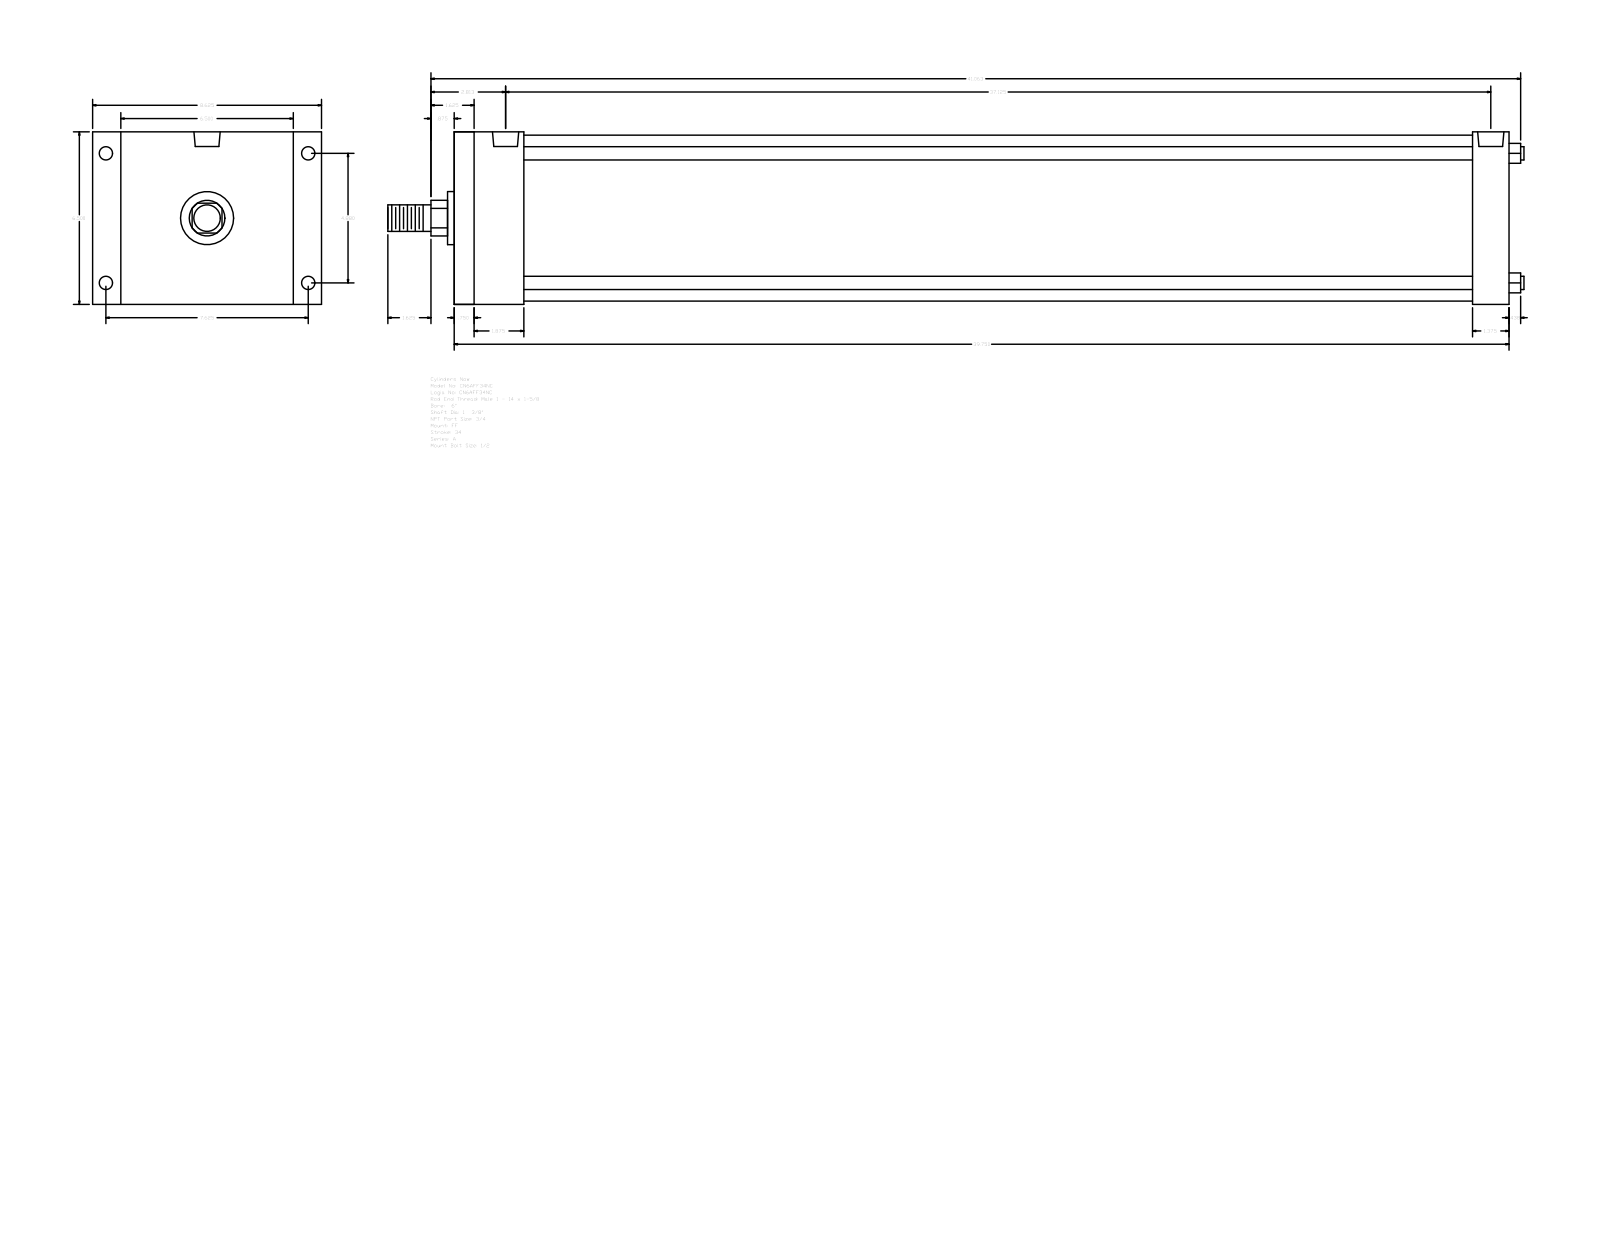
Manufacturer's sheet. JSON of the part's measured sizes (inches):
{"part_name": "A_FF__0600_1.375", "step_written_by": "GSSL Pune (CONFIG_CONTROL_DESIGN)", "units": "inches", "bodies": {"solids": 0, "faces": 92, "planar": 64, "cylindrical": 28, "other": 0}, "overall_size": [42.813, 8.625, 6.5], "round_holes": [[0.5, 4], [0.594, 4], [0.989, 2]], "round_bosses_or_shafts": [[0.5, 4], [6.25, 1], [2, 1], [1.375, 1], [1, 1]], "partial_cylinders_radius": [[0.672, 1]], "face_to_face_distances": [6.5, 39.75, 0.75, 39, 2.625, 1.875, 37.125, 38.375, 37.625, 35.75], "hole_center_spacings": [0.219, 4.88, 7.625, 9.053, 36.687, 36.906, 37.125]}
